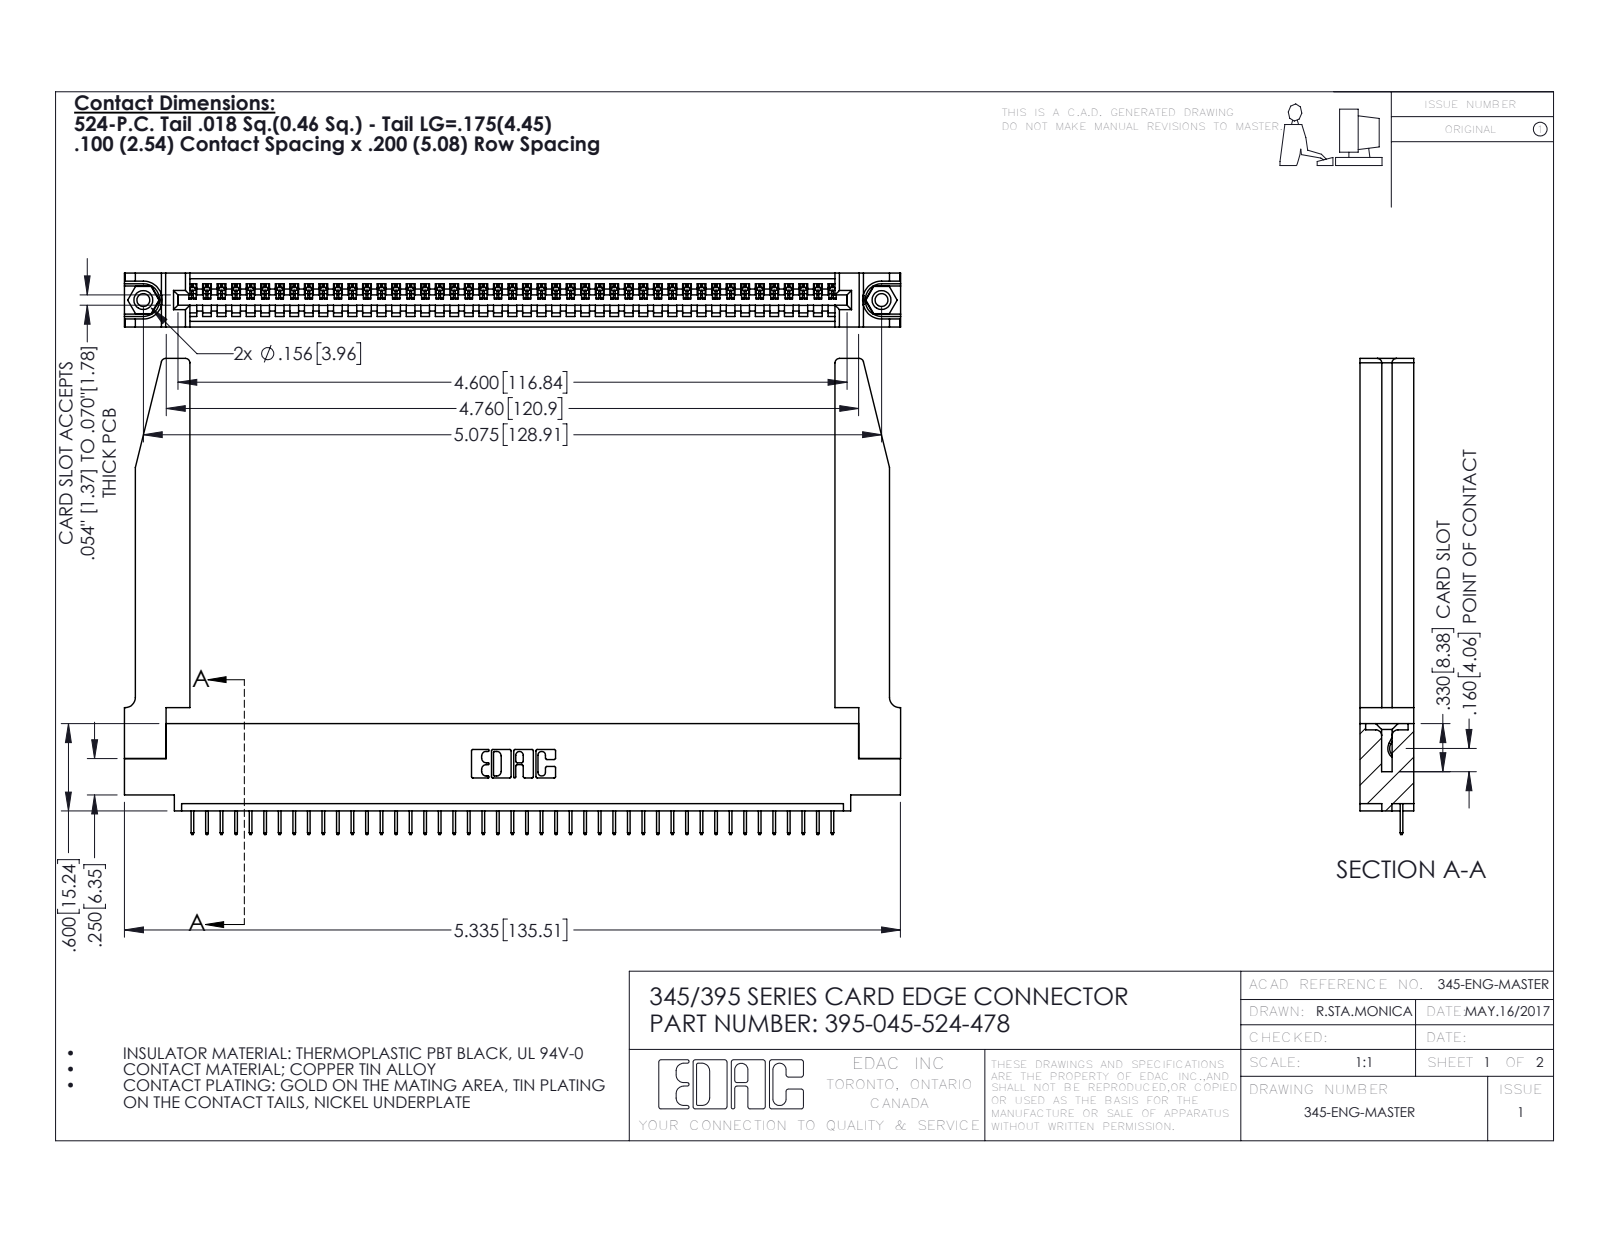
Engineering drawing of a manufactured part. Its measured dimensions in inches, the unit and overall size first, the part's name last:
Units: inches
Overall size (bounding box): 5.336 × 3.272 × 0.37
Round holes (diameter × count): ⌀0.089 ×2, ⌀0.125 ×2, ⌀0.156 ×2, ⌀0.064 ×1
Round bosses / shafts (diameter × count): ⌀0.155 ×2
Partial cylindrical surfaces — rounded edges, fillets, slot ends (radius × count): R0.006 ×90, R0.01 ×22, R0.03 ×8, R0.007 ×6, R0.031 ×6, R0.026 ×3, R0.031 ×2, R0.04 ×2
Main face-to-face distances: 0.37, 0.072, 0.298, 0.2, 0.098, 0.272, 0.025, 0.225, 0.148, 0.15
Hole centre spacings: 0.27, 4.839, 5.075
Volume: 1.246 in³ · Surface area: 35.97 in²
Bodies: 50 solids, 3154 faces (2296 planar, 806 cylindrical, 52 other)
Part name (STEP PRODUCT): 345-220-078_345-220-078; 345 Part_0.110 Offset - 0.156 Dia-TH; 345-250-001_345-250-001-102; 345-292-001_345-293-124 (+1 more)
STEP written by: SolidWorks 2016 (CONFIG_CONTROL_DESIGN)
